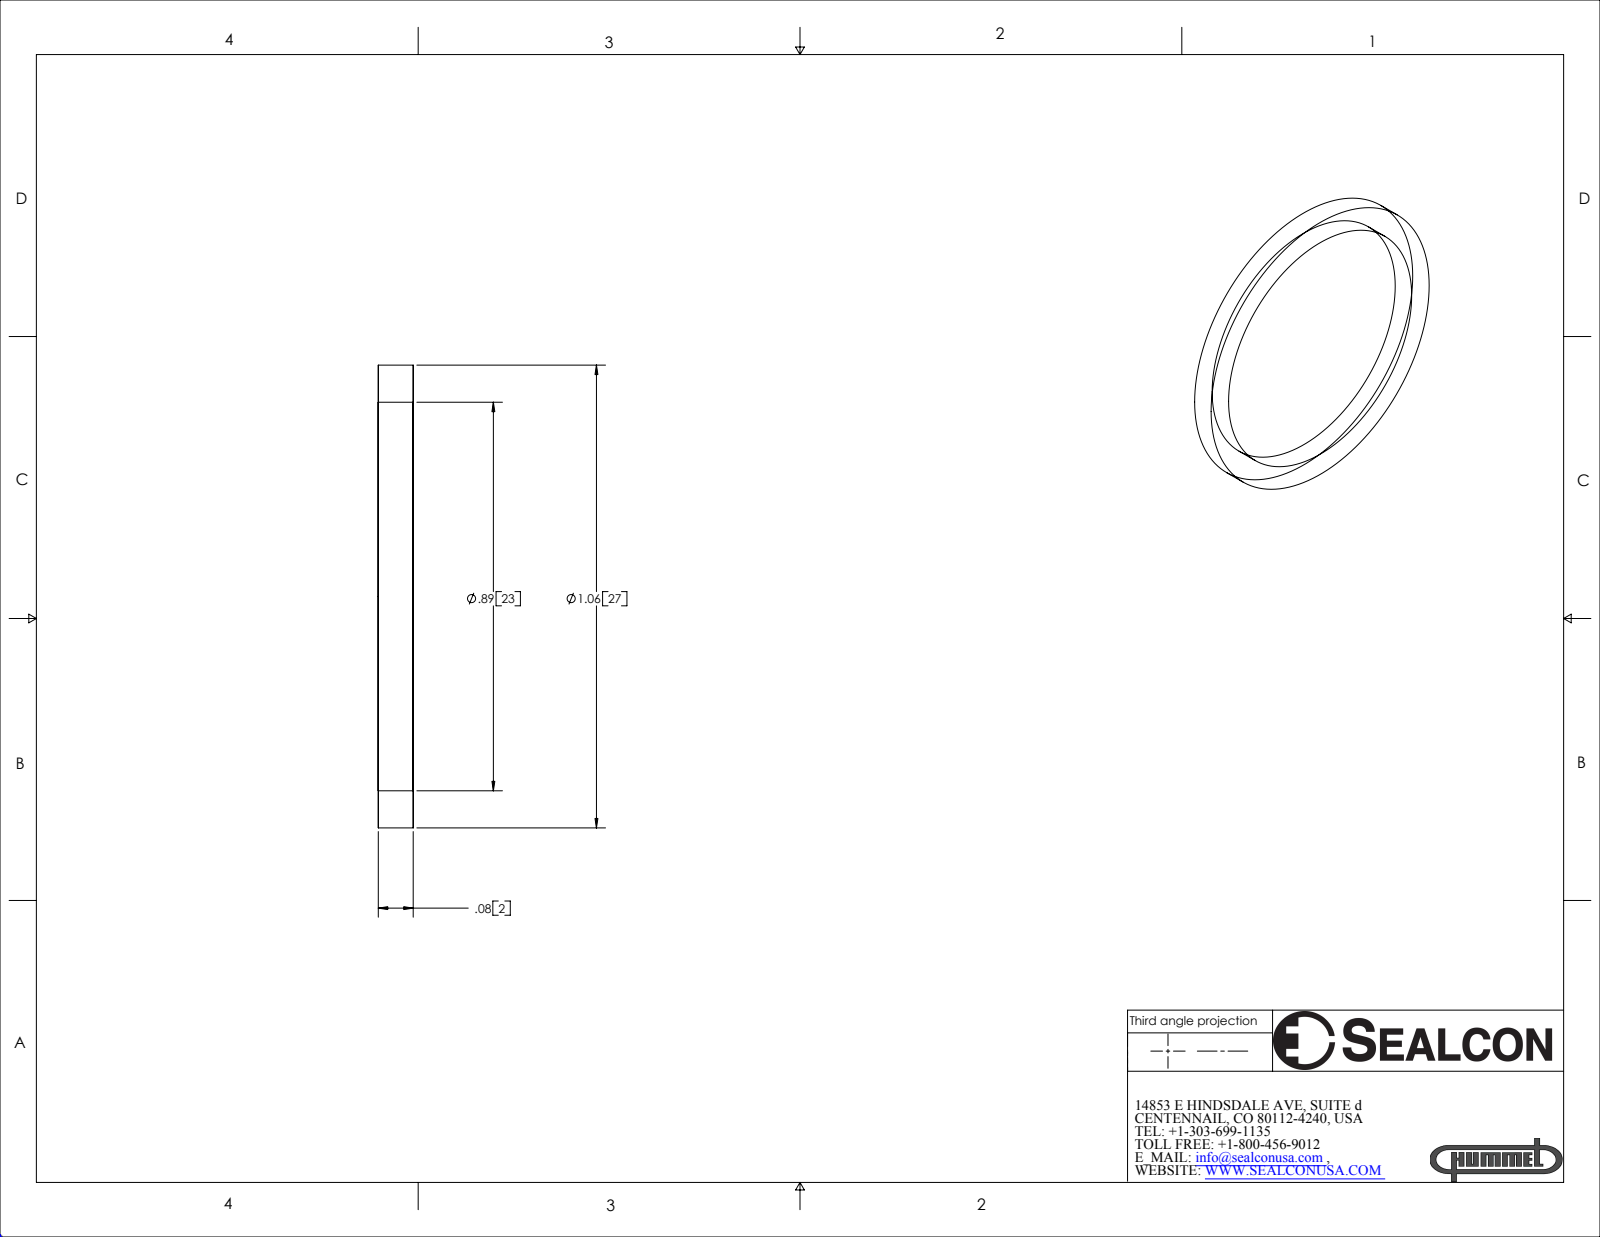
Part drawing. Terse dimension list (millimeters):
name: SR-16-NY
written by: SolidWorks 2007 (CONFIG_CONTROL_DESIGN)
unit: mm
bodies: 1 solid, 6 faces (2 planar, 4 cylindrical, 0 other)
size: 26.9 × 26.9 × 2
volume: 340 mm³; area: 652 mm²
holes: 1× ⌀22.6
bosses: 1× ⌀26.9
face distances: 2
